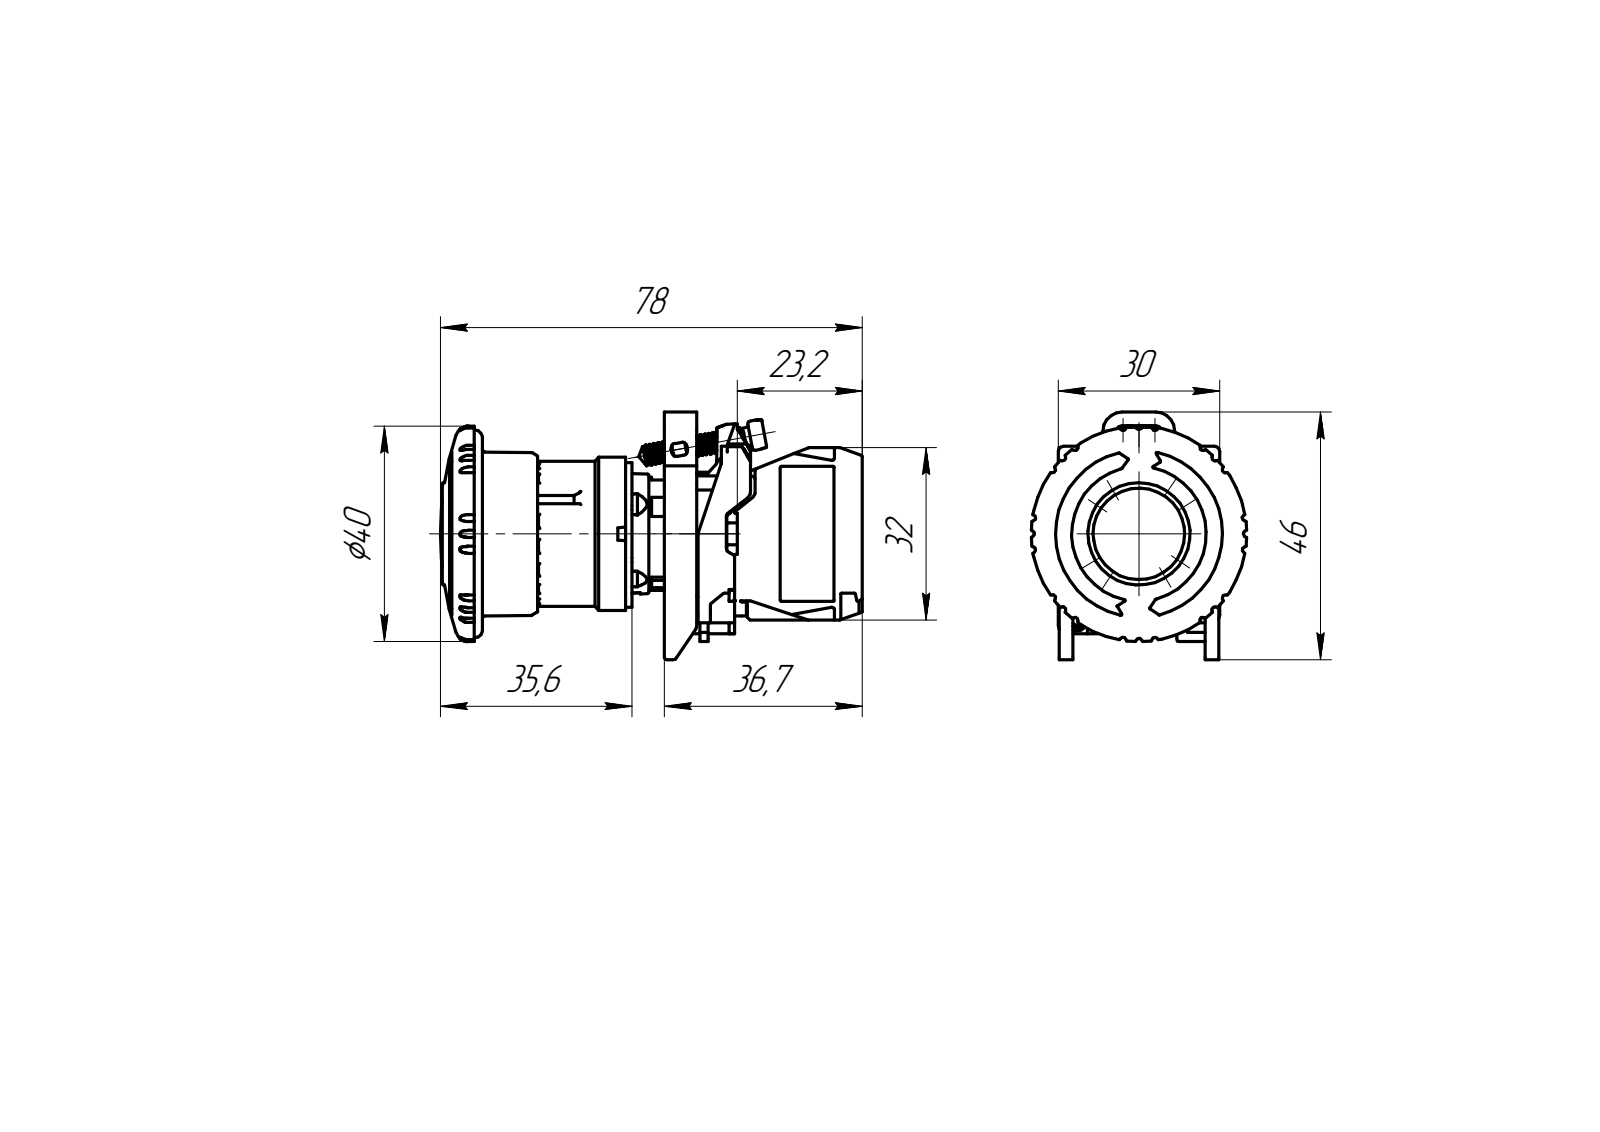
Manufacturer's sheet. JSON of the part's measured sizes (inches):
{"part_name": "ZB4BE009; ZBE102; ZB4BS54C; XB4BS542_ASM", "step_written_by": "PRO/ENGINEER BY PARAMETRIC TECHNOLOGY CORPORATION, 2010280 (AUTOMOTIVE_DESIGN)", "units": "inches", "bodies": {"solids": 14, "faces": 3707, "planar": 2099, "cylindrical": 1091, "other": 517}, "overall_size": [3.083, 1.811, 1.574], "volume_in3": 2.493, "surface_area_in2": 33.25, "round_holes": [[0.098, 8], [0.075, 4], [0.114, 4], [0.157, 4], [0.102, 2], [0.059, 1], [0.669, 1], [1.22, 1]], "round_bosses_or_shafts": [[0.106, 4], [0.22, 2], [0.114, 2], [0.094, 2], [1.118, 1], [1.059, 1], [0.984, 1], [0.827, 1]], "partial_cylinders_radius": [[0.008, 220], [0.012, 72], [0.004, 68], [0.006, 62], [0.02, 55], [0.039, 36], [0.022, 24], [0.016, 11]], "face_to_face_distances": [0.098, 0.236, 0.039, 0.106, 0.472, 0.512, 0.276, 0.386, 1.075, 0.059], "hole_center_spacings": [0.157, 0.232, 0.24, 0.431, 0.465, 0.481, 0.537, 0.625]}
